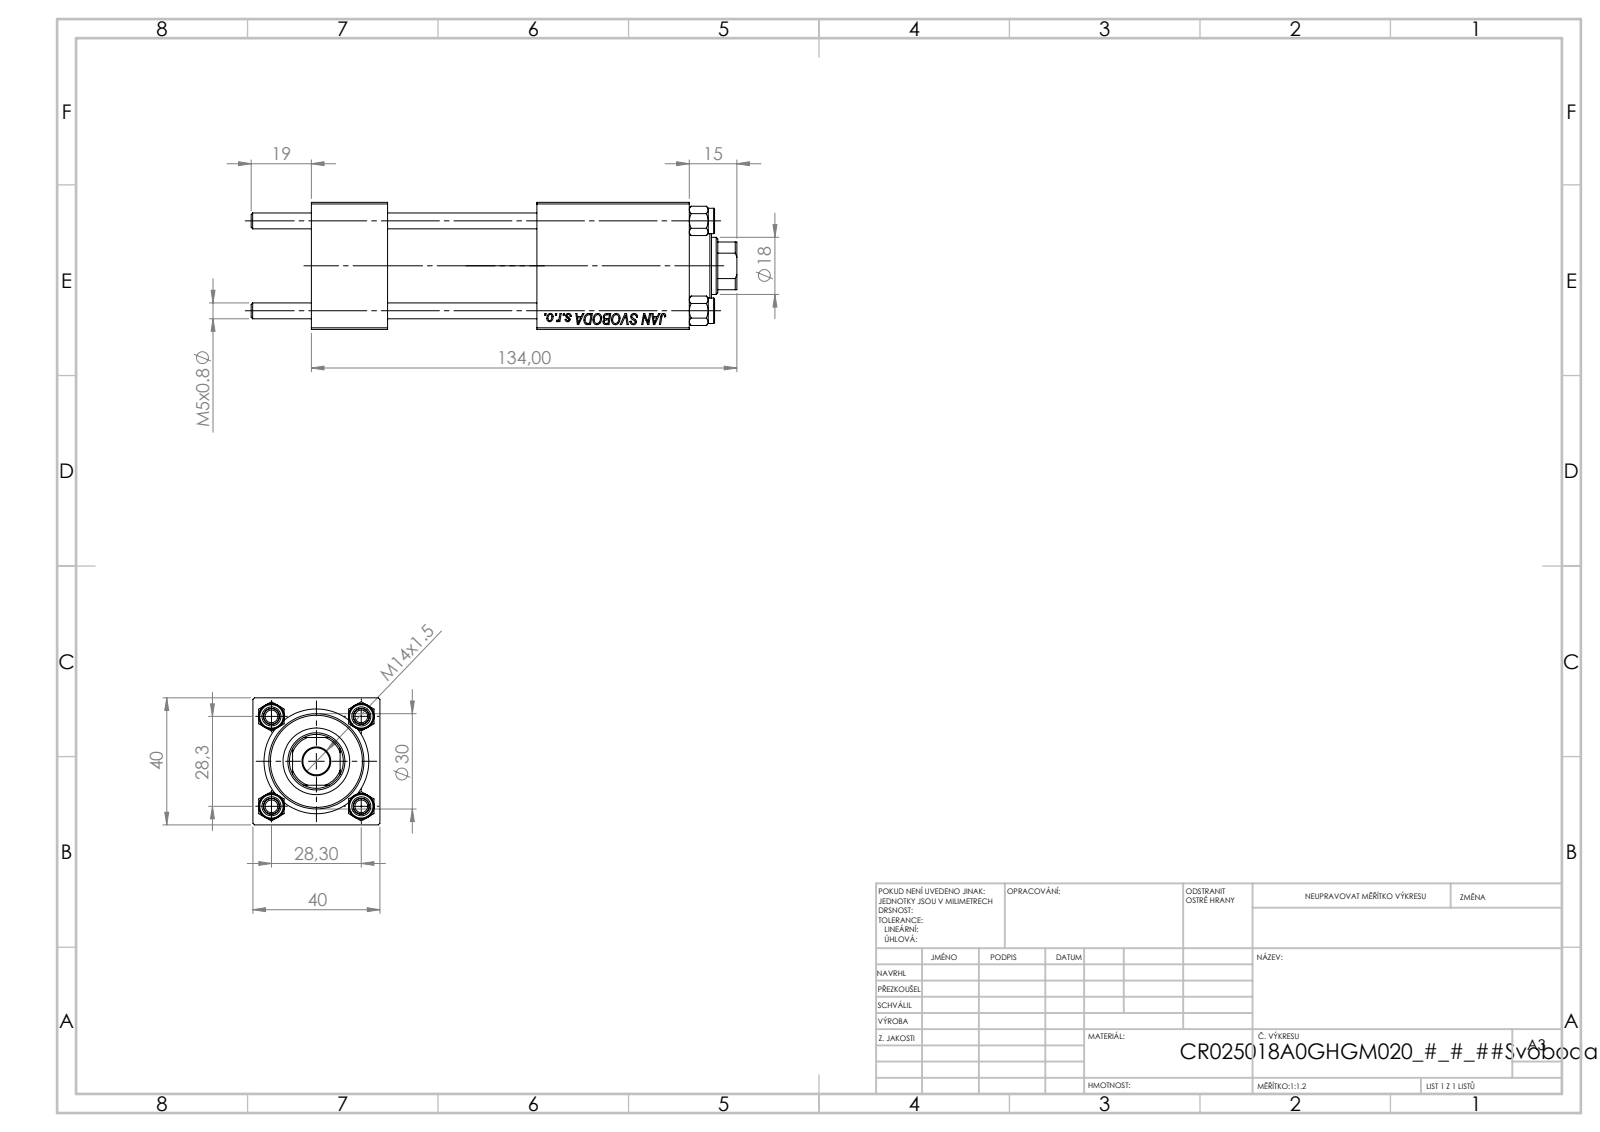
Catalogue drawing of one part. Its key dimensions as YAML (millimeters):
part_name: "V215CR_VCP; V215CR_BODY_A; NUT_M5; V215_VC_A (+1 more)"
step_written_by: "SolidWorks 2019 (CONFIG_CONTROL_DESIGN)"
units: millimeters
bodies: {solids: 11, faces: 1128, planar: 516, cylindrical: 76, other: 536}
overall_size: [153, 40, 40]
volume: 152431
surface_area: 61147
round_holes:
  - {diameter: 5, count: 4}
  - {diameter: 20, count: 3}
  - {diameter: 7, count: 2}
  - {diameter: 13.16, count: 2}
  - {diameter: 8.5, count: 1}
  - {diameter: 18, count: 1}
  - {diameter: 21, count: 1}
  - {diameter: 25, count: 1}
  - {diameter: 30, count: 1}
round_bosses_or_shafts:
  - {diameter: 8, count: 4}
  - {diameter: 31, count: 1}
partial_cylinders:
  - {radius: 8.5, count: 1}
face_to_face_distances: [40, 24, 71, 47, 90.3, 66.3, 19.3, 119, 95, 48]
hole_center_spacings: [20.01, 28.3, 40.02, 72]
